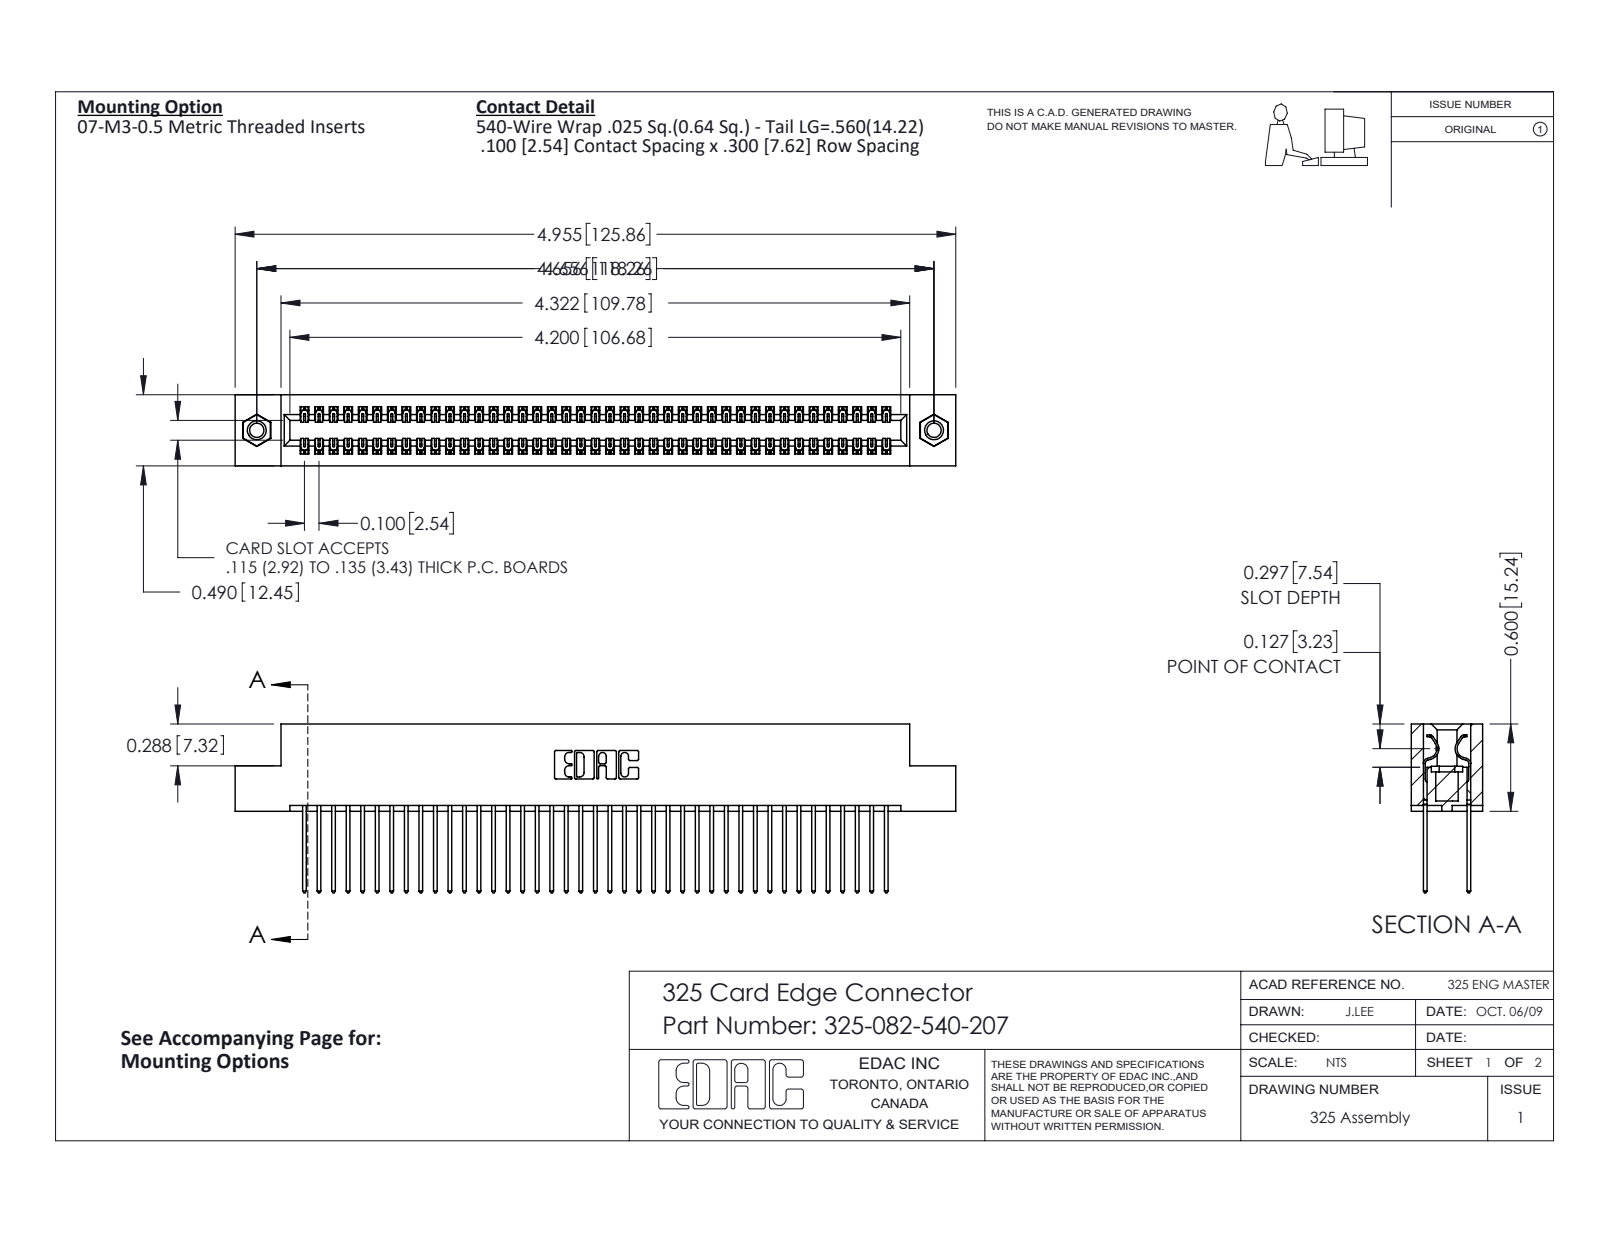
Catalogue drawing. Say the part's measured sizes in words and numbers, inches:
The part is named "325-082-540-207; 345-250-001_345-250-005-103; 325-292-001_325-293-140; 325 Part_TI". Its 3-D file was written by "SolidWorks 2016 (CONFIG_CONTROL_DESIGN)". It is 85 solids with 4438 faces: 3054 planar, 1368 cylindrical and 16 other. Overall it measures 4.955 by 1.16 by 0.49 inches. Its volume is 1.009 cubic inches and its surface area 33.32 square inches. Round holes: 2 of diameter 0.098, 2 of diameter 0.125, 2 of diameter 0.16. Round bosses or shafts: 2 of diameter 0.155. Partial cylindrical surfaces (rounded edges, fillets, slot ends): 123 of radius 0.006, 82 of radius 0.01, 22 of radius 0.01, 6 of radius 0.007, 6 of radius 0.031, 3 of radius 0.026, 2 of radius 0.014, 2 of radius 0.022. The main face-to-face distances are 0.083, 0.407, 0.3, 0.107, 0.383, 0.025, 0.49, 0.325, 0.275, 0.56. The hole center spacings are 4.656.
